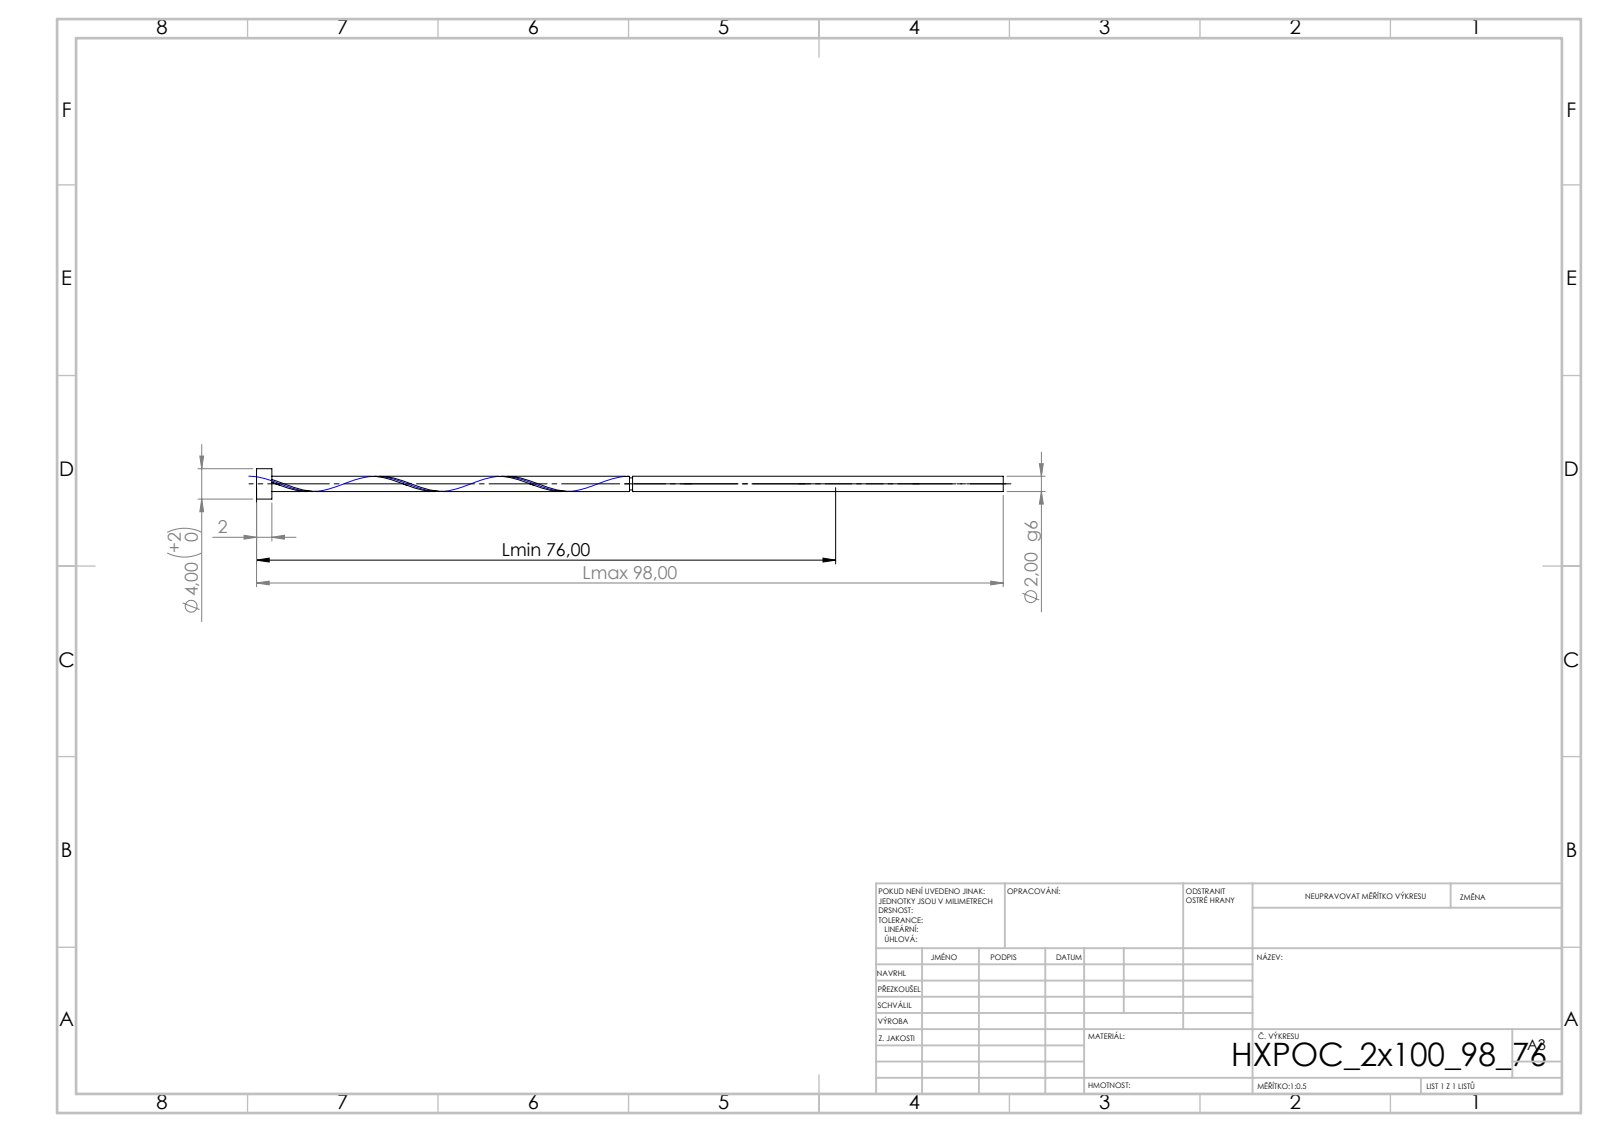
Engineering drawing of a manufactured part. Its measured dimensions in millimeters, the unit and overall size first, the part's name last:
Units: millimetres
Overall size (bounding box): 98 × 4 × 4
Round bosses / shafts (diameter × count): ⌀4 ×1, ⌀2 ×1, ⌀1.6 ×1
Main face-to-face distances: 2, 98, 96, 49.34, 47.34, 48.66, 48.94, 46.94, 0.4, 49.06
Volume: 323 mm³ · Surface area: 667 mm²
Bodies: 1 solid, 22 faces (5 planar, 15 cylindrical, 2 other)
STEP written by: SolidWorks 2019 (CONFIG_CONTROL_DESIGN)
